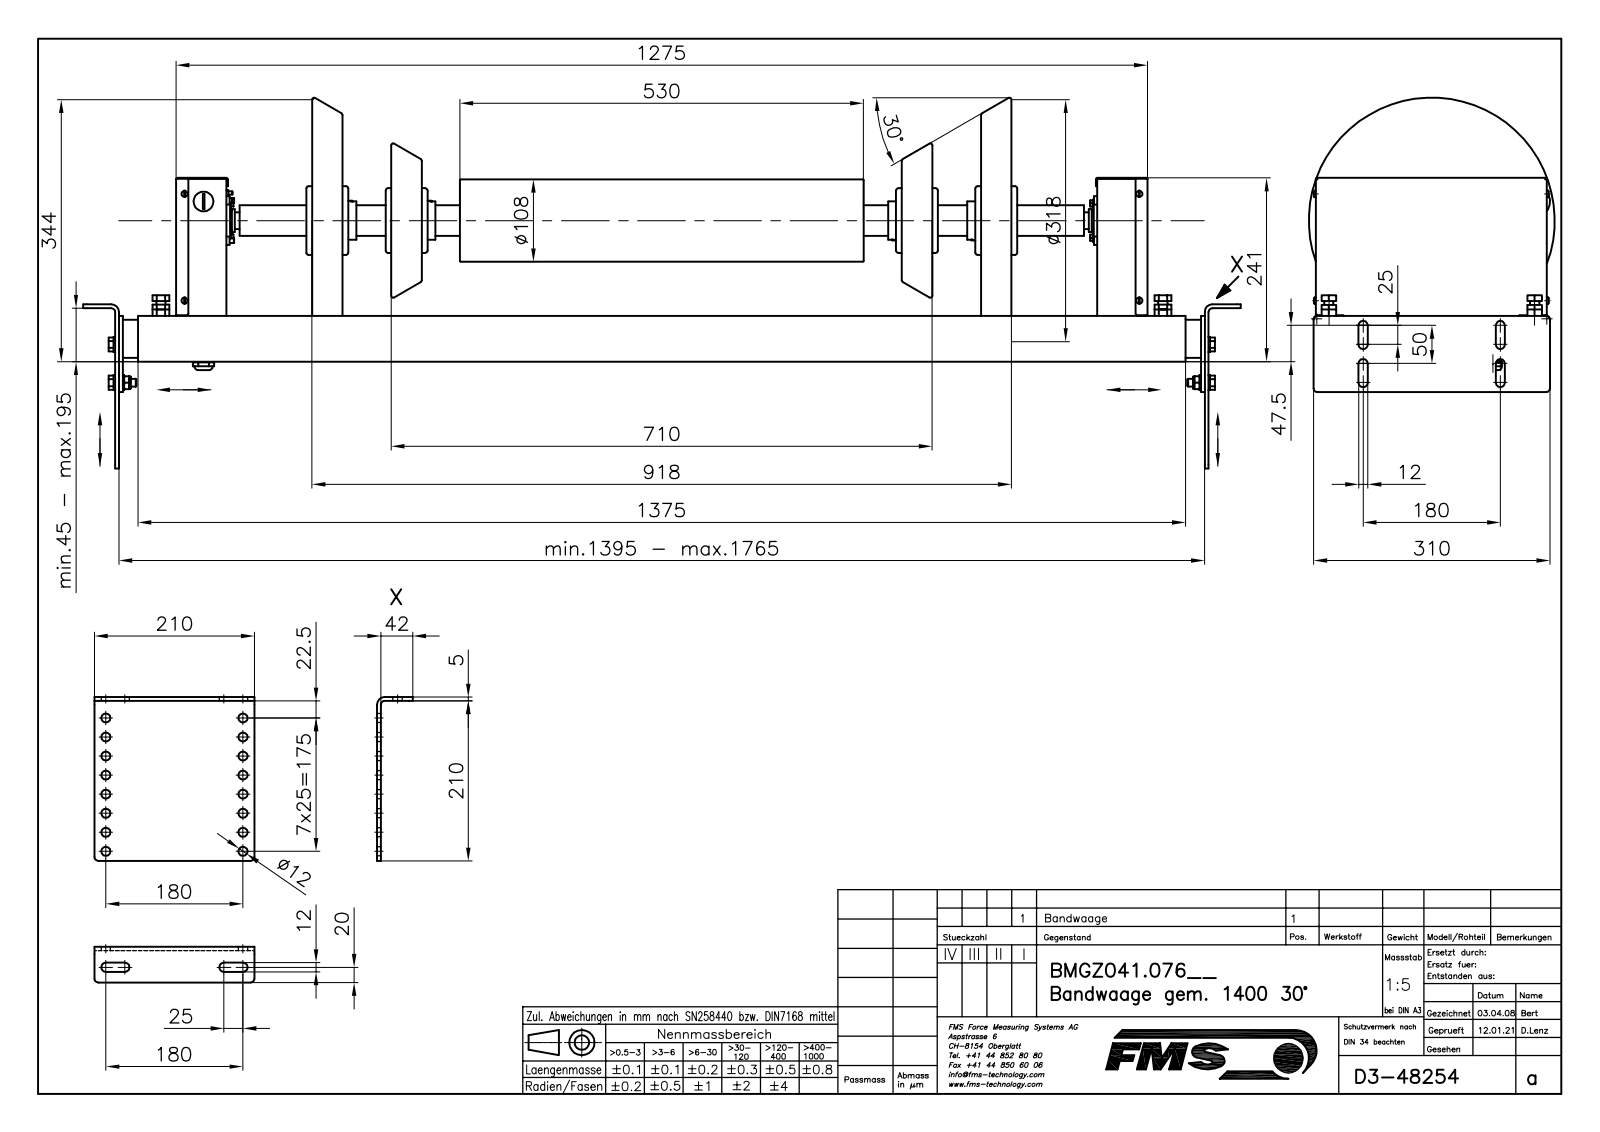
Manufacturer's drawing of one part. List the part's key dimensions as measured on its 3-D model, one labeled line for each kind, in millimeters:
Part name (STEP PRODUCT): B48254_STP; B50110; 6KT-SCHRAUBE_M12X30; ZYL_SCHR__M4X8 (+8 more)
STEP written by: Mechanical Desktop 2009 (CONFIG_CONTROL_DESIGN)
Units: millimetres
Bodies: 179 solids, 2980 faces (1435 planar, 1070 cylindrical, 475 other)
Overall size (bounding box): 1519 × 486.26 × 322.53
Volume: 9 360 000 mm³ · Surface area: 4 287 000 mm²
Round holes (diameter × count): ⌀12 ×17, ⌀5 ×6, ⌀3.5 ×4, ⌀4.9 ×4, ⌀6.4 ×4, ⌀6.91 ×4, ⌀8.68 ×4, ⌀8.75 ×4, ⌀10 ×4, ⌀10.5 ×4, ⌀10.68 ×4, ⌀14.8 ×4
Round bosses / shafts (diameter × count): ⌀12 ×11, ⌀8.2 ×8, ⌀4.2 ×8, ⌀20 ×6, ⌀10 ×6, ⌀8 ×6, ⌀5 ×5, ⌀16 ×4
Partial cylindrical surfaces — rounded edges, fillets, slot ends (radius × count): R2 ×34, R1 ×24, R4 ×16, R5 ×16, R6 ×12, R3.5 ×8, R2.25 ×6, R0.5 ×4
Main face-to-face distances: 4, 5, 1, 270, 36, 3, 266, 32, 56, 66
Hole centre spacings: 25, 181.73, 50, 186.82, 75, 195, 100, 180
